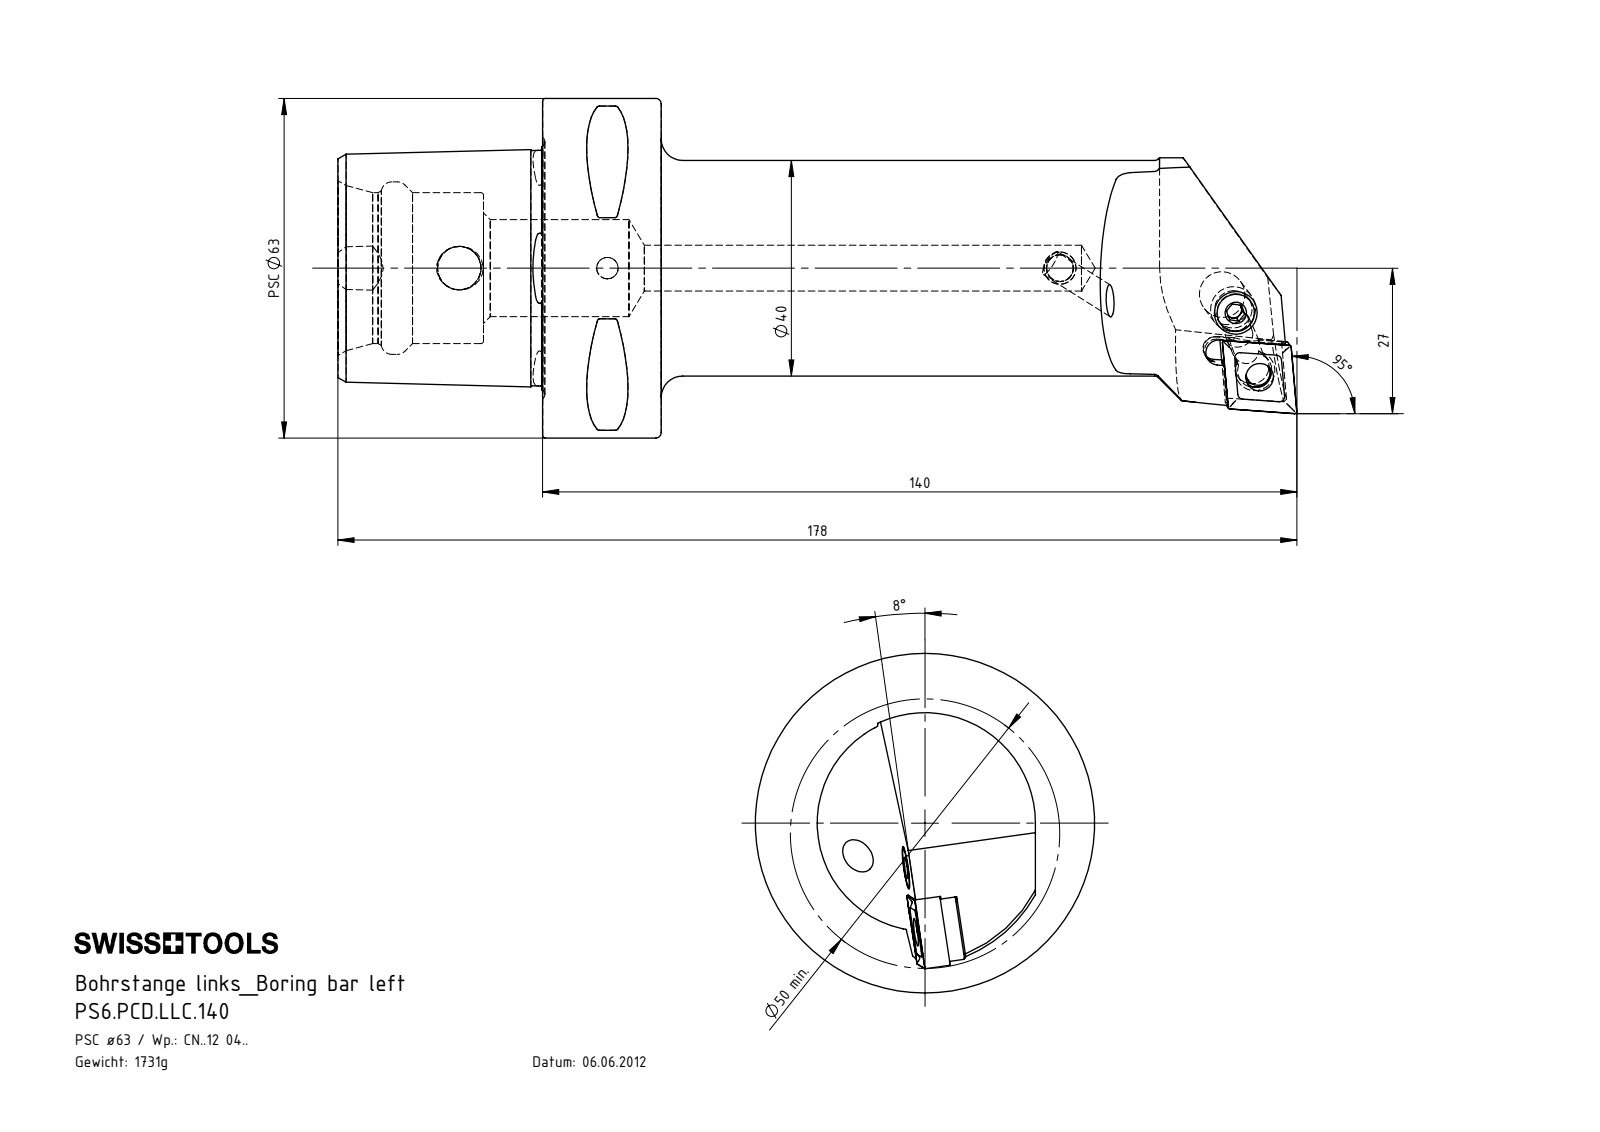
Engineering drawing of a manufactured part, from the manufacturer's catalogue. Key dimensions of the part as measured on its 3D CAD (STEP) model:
Part name (STEP PRODUCT): PS6-PCD.LLC.140; WCD-ER1.101.000; WCD-ER4.101.017_A; WCD-ER2.101.003_A (+4 more)
STEP written by: SolidWorks 2012 (CONFIG_CONTROL_DESIGN)
Units: millimetres
Bodies: 8 solids, 358 faces (94 planar, 89 cylindrical, 175 other)
Overall size (bounding box): 178 × 63 × 63
Volume: 219 784 mm³ · Surface area: 39 244 mm²
Round holes (diameter × count): ⌀5 ×2, ⌀4 ×1, ⌀5.16 ×1, ⌀6.4 ×1, ⌀7 ×1, ⌀8.1 ×1, ⌀8.4 ×1, ⌀8.5 ×1, ⌀18 ×1, ⌀28 ×1, ⌀32 ×1
Round bosses / shafts (diameter × count): ⌀63 ×1, ⌀40 ×1, ⌀8 ×1, ⌀7.9 ×1, ⌀6.4 ×1, ⌀6 ×1, ⌀4.5 ×1, ⌀3.55 ×1
Partial cylindrical surfaces — rounded edges, fillets, slot ends (radius × count): R0.5 ×8, R0.4 ×4, R1 ×4, R2.5 ×2, R6 ×2, R2.1 ×1, R2.2 ×1, R2.35 ×1
Main face-to-face distances: 22, 38, 60, 24.88, 27, 11, 33, 4.49, 55.8, 3.18
Hole centre spacings: 12.81, 12.87, 27.5, 84, 111.5
